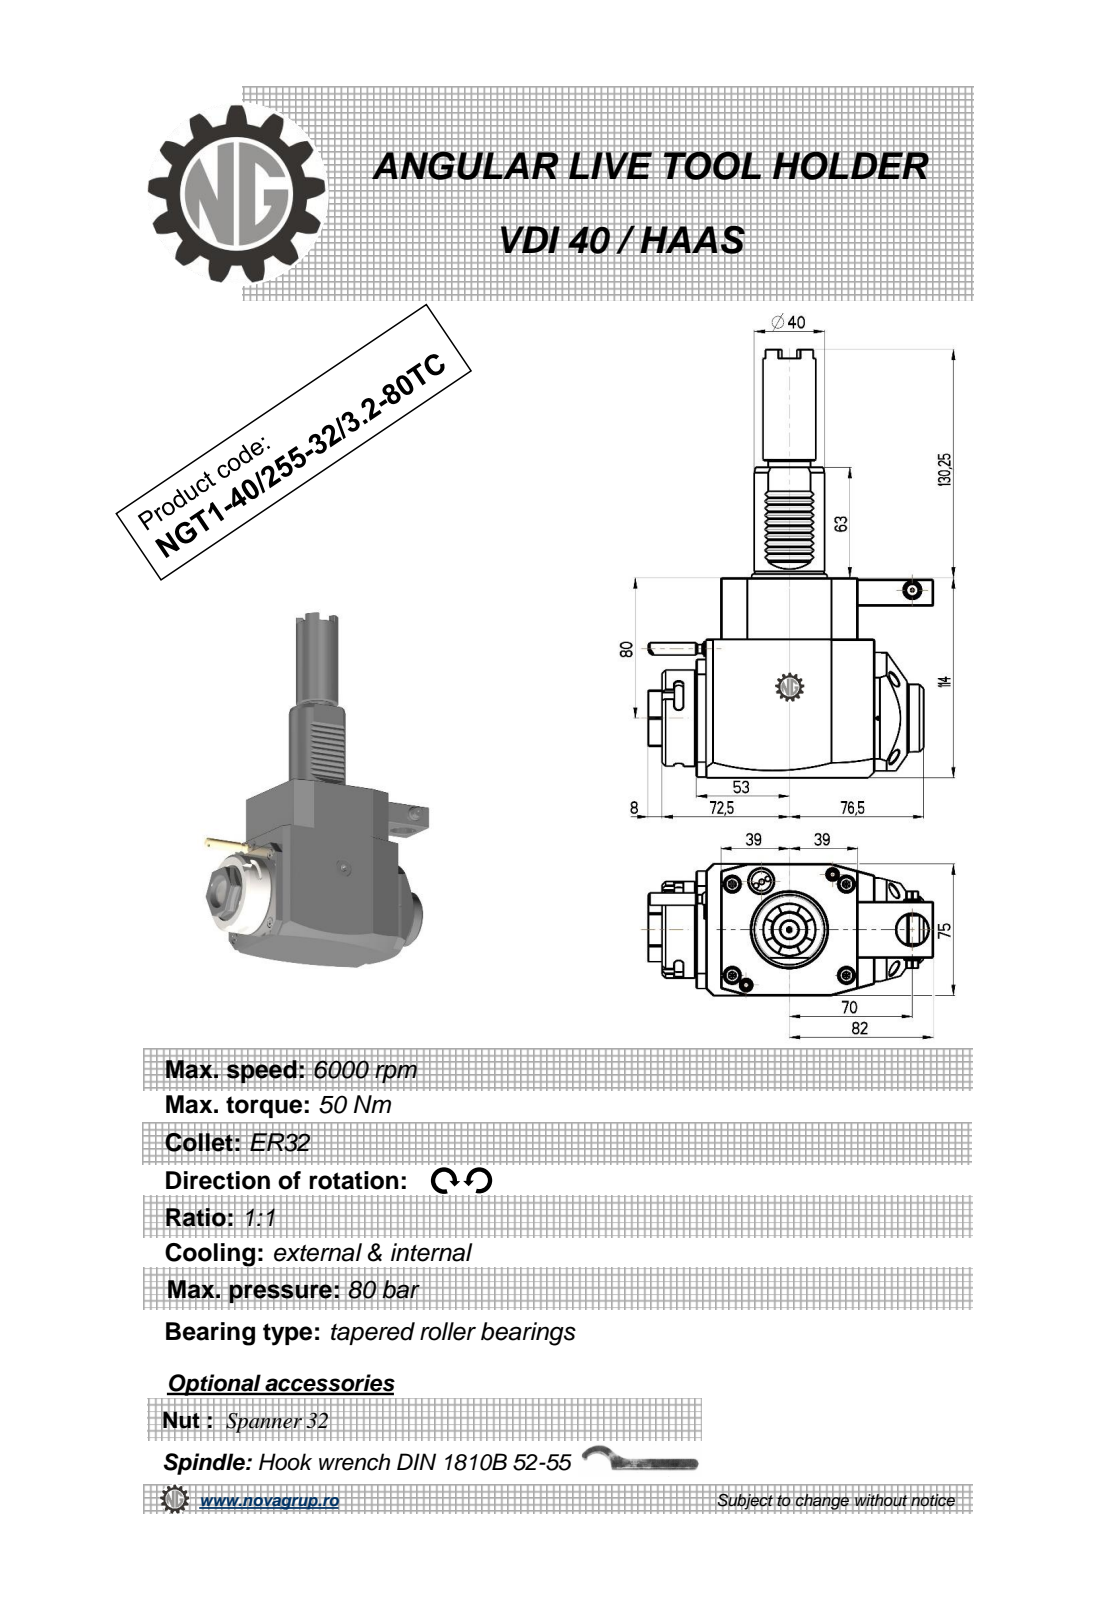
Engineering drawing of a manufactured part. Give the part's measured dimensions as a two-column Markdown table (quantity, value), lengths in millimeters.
| quantity | value |
| --- | --- |
| part name | NGT1_40_255_32_3_2_80TC |
| STEP written by | PRO/ENGINEER BY PARAMETRIC TECHNOLOGY CORPORATION, 2010280 (CONFIG_CONTROL_DESIGN) |
| units | millimeters |
| bodies | 1 solid, 391 faces (219 planar, 82 cylindrical, 90 other) |
| overall size | 244.25 × 162.5 × 75 |
| volume | 1 020 000 mm³ |
| surface area | 81 608 mm² |
| round holes (diameter × count) | 2 × 1, 2.5 × 1, 3 × 1, 9.5 × 1, 18 × 1, 20 × 1, 23 × 1 |
| round bosses / shafts (diameter × count) | 8.96 × 2, 55 × 1, 48 × 1, 40 × 1, 38.5 × 1, 30 × 1, 24 × 1, 10 × 1 |
| partial cylindrical surfaces (radius × count) | 0.3 × 10, 2.5 × 6, 180 × 2, 0.5 × 1, 3.85 × 1, 4.25 × 1, 24.5 × 1, 37.5 × 1 |
| main face-to-face distances | 75, 114, 14, 33.5, 79, 92, 78, 21.5, 98, 19.5 |
| hole center spacings | 37.35, 43.2, 70, 72.5 |
